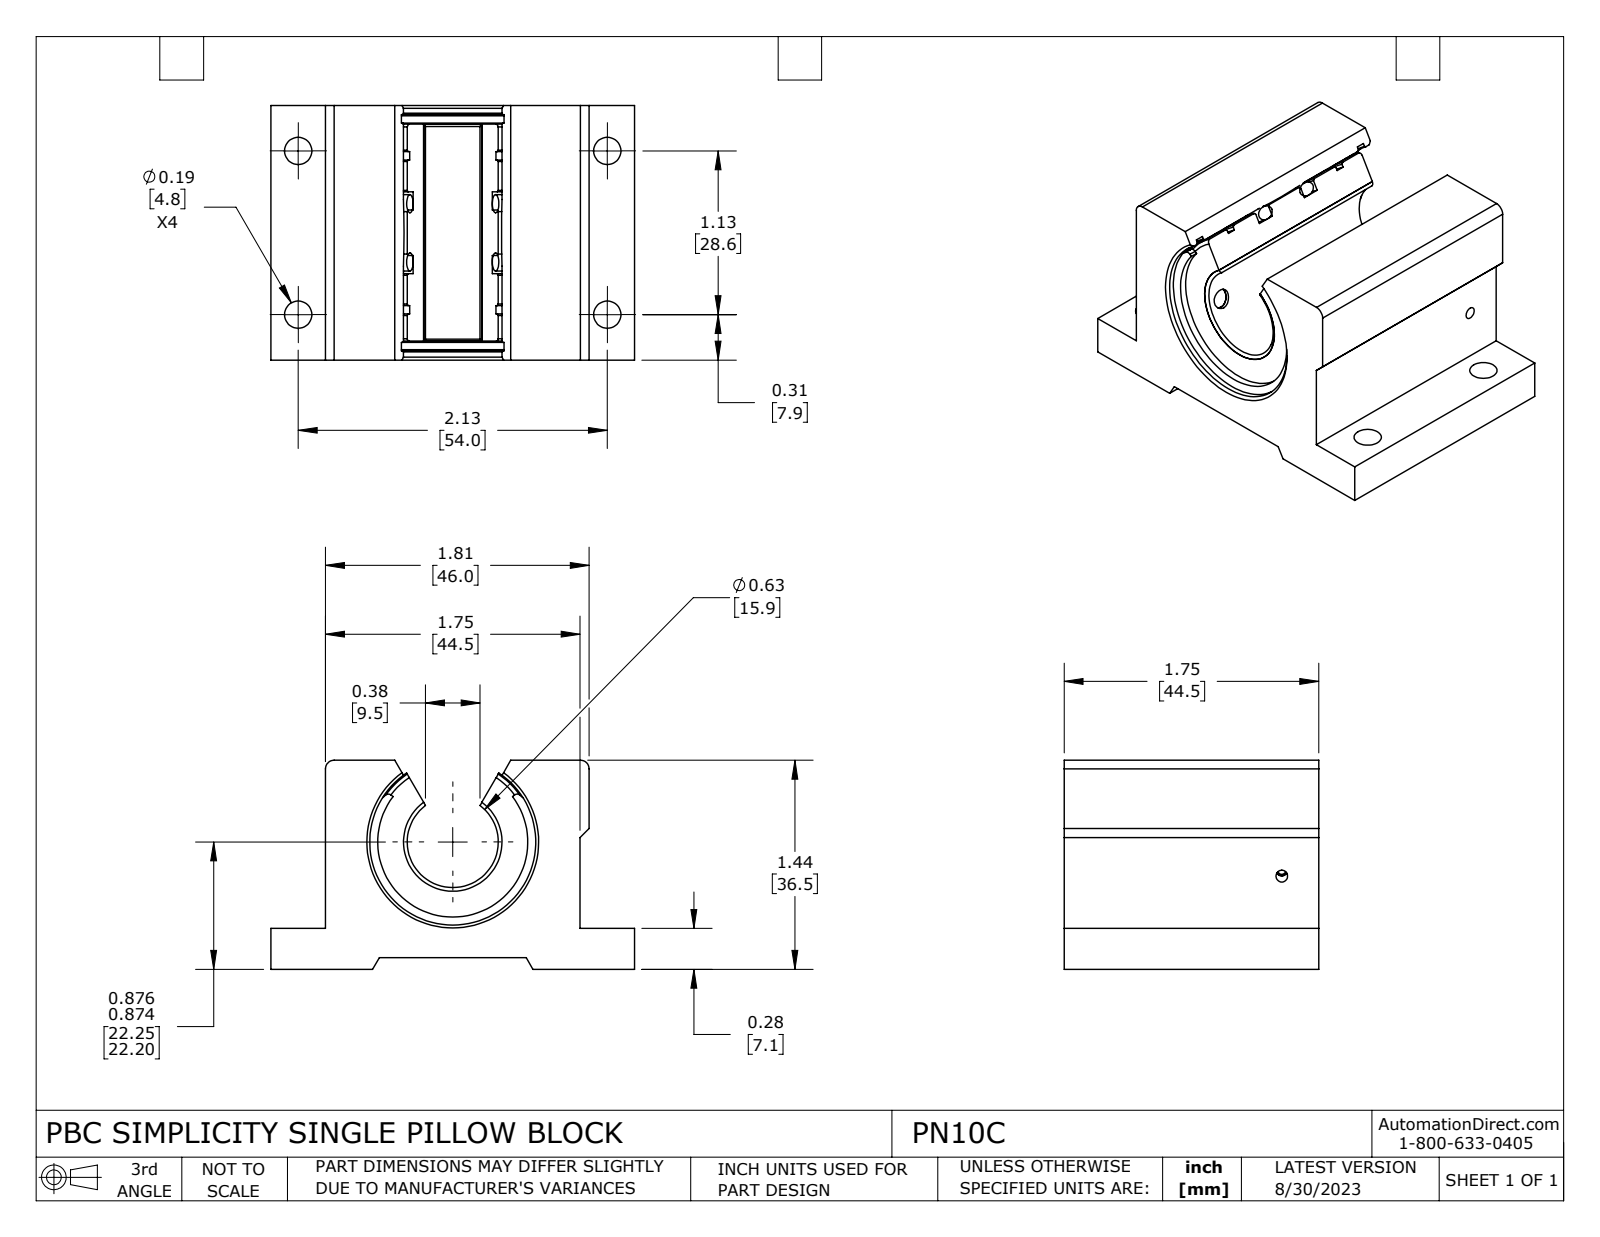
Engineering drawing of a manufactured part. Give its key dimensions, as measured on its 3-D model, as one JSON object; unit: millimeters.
{"part_name": "PN10C", "step_written_by": "SolidWorks 2021 (CONFIG_CONTROL_DESIGN)", "units": "millimeters", "bodies": {"solids": 8, "faces": 207, "planar": 54, "cylindrical": 94, "other": 59}, "overall_size": [63.5, 44.5, 36.5], "volume_mm3": 59470, "surface_area_mm2": 25690, "round_holes": [[4.7, 4], [1.4, 1], [2, 1], [3.5, 1], [15.9, 1], [17.2, 1], [29, 1], [30.4, 1]], "round_bosses_or_shafts": [[28.5, 1], [26.9, 1], [24.4, 1], [2, 1]], "partial_cylinders_radius": [[0.8, 2], [1.5, 2], [4.6, 2], [13.1, 1], [15.5, 1]], "face_to_face_distances": [44.5, 2, 36.5, 34.5, 7.1, 5.1, 29.4, 9.5, 54, 3.3], "hole_center_spacings": [28.6, 54, 61.1]}
